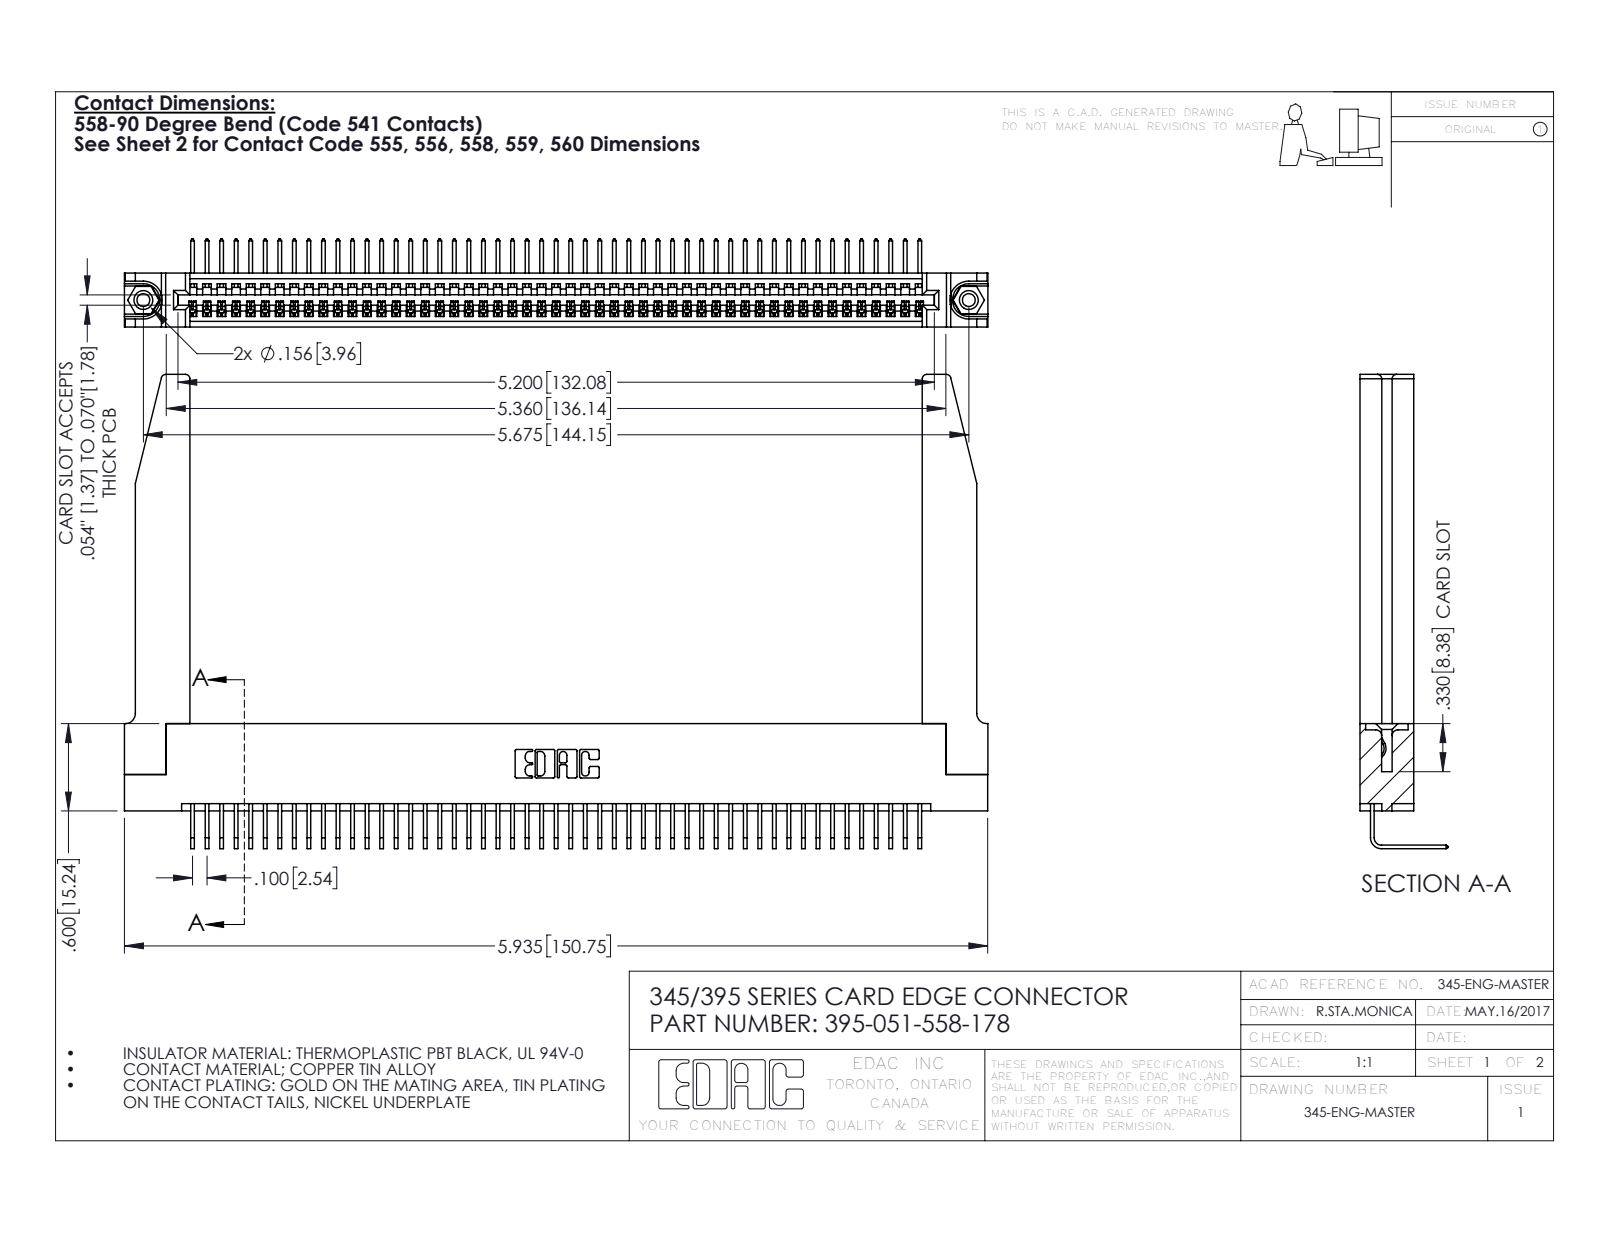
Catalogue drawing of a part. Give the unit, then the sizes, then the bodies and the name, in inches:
Units: inches
Overall size (bounding box): 5.936 × 3.259 × 0.605
Round holes (diameter × count): ⌀0.089 ×2, ⌀0.125 ×2, ⌀0.156 ×2, ⌀0.064 ×1
Round bosses / shafts (diameter × count): ⌀0.155 ×2
Partial cylindrical surfaces — rounded edges, fillets, slot ends (radius × count): R0.006 ×102, R0.01 ×22, R0.03 ×8, R0.007 ×6, R0.031 ×6, R0.026 ×3, R0.031 ×2, R0.04 ×2
Main face-to-face distances: 0.37, 0.072, 0.298, 0.2, 0.098, 0.272, 0.025, 0.225, 0.148, 0.15
Hole centre spacings: 0.27, 5.439, 5.675
Volume: 1.363 in³ · Surface area: 42.35 in²
Bodies: 56 solids, 3420 faces (2364 planar, 1004 cylindrical, 52 other)
Part name (STEP PRODUCT): 345-292-001_558 Tail - 2; 345 Part_Flush Mounting Lugs - 0.156 Dia-TH; 345-220-078_345-220-078; 395-051-558-178 (+1 more)
STEP written by: SolidWorks 2016 (CONFIG_CONTROL_DESIGN)
